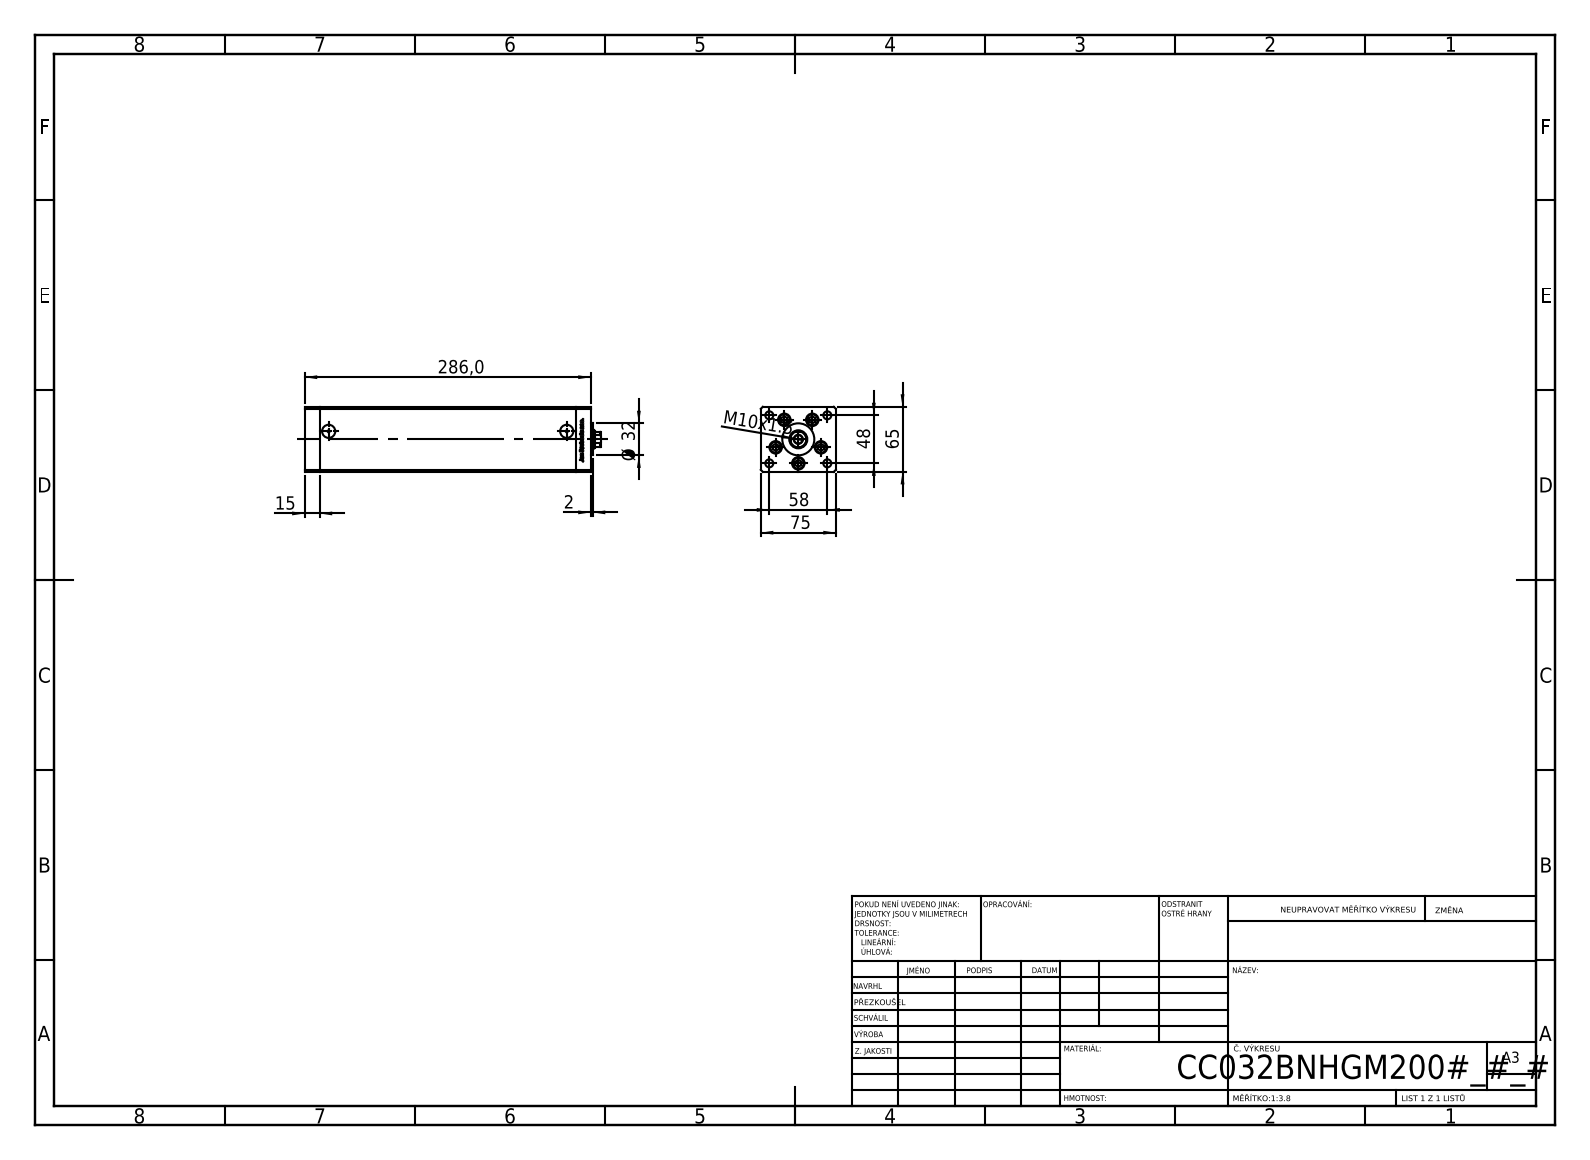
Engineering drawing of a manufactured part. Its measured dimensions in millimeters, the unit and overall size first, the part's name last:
Units: millimetres
Overall size (bounding box): 296 × 75 × 65
Round holes (diameter × count): ⌀9 ×5, ⌀12.5 ×5, ⌀8 ×4, ⌀2 ×2, ⌀13.16 ×2, ⌀8.5 ×1, ⌀18 ×1
Round bosses / shafts (diameter × count): ⌀8 ×5, ⌀32 ×1
Partial cylindrical surfaces — rounded edges, fillets, slot ends (radius × count): R0.93 ×2, R8.5 ×1
Main face-to-face distances: 75, 65, 15, 256, 271, 54.5, 10.5, 26.25, 48.75, 286
Hole centre spacings: 24, 37.64, 15.67, 17.22, 27.71, 28.83, 29, 32.63
Volume: 1 217 000 mm³ · Surface area: 182 157 mm²
Bodies: 14 solids, 1183 faces (462 planar, 147 cylindrical, 574 other)
Part name (STEP PRODUCT): ALLEN BOLT; V220C_FRONT_B; V220C_B MIDDLE; V220C BACK_B (+1 more)
STEP written by: SolidWorks 2019 (CONFIG_CONTROL_DESIGN)
